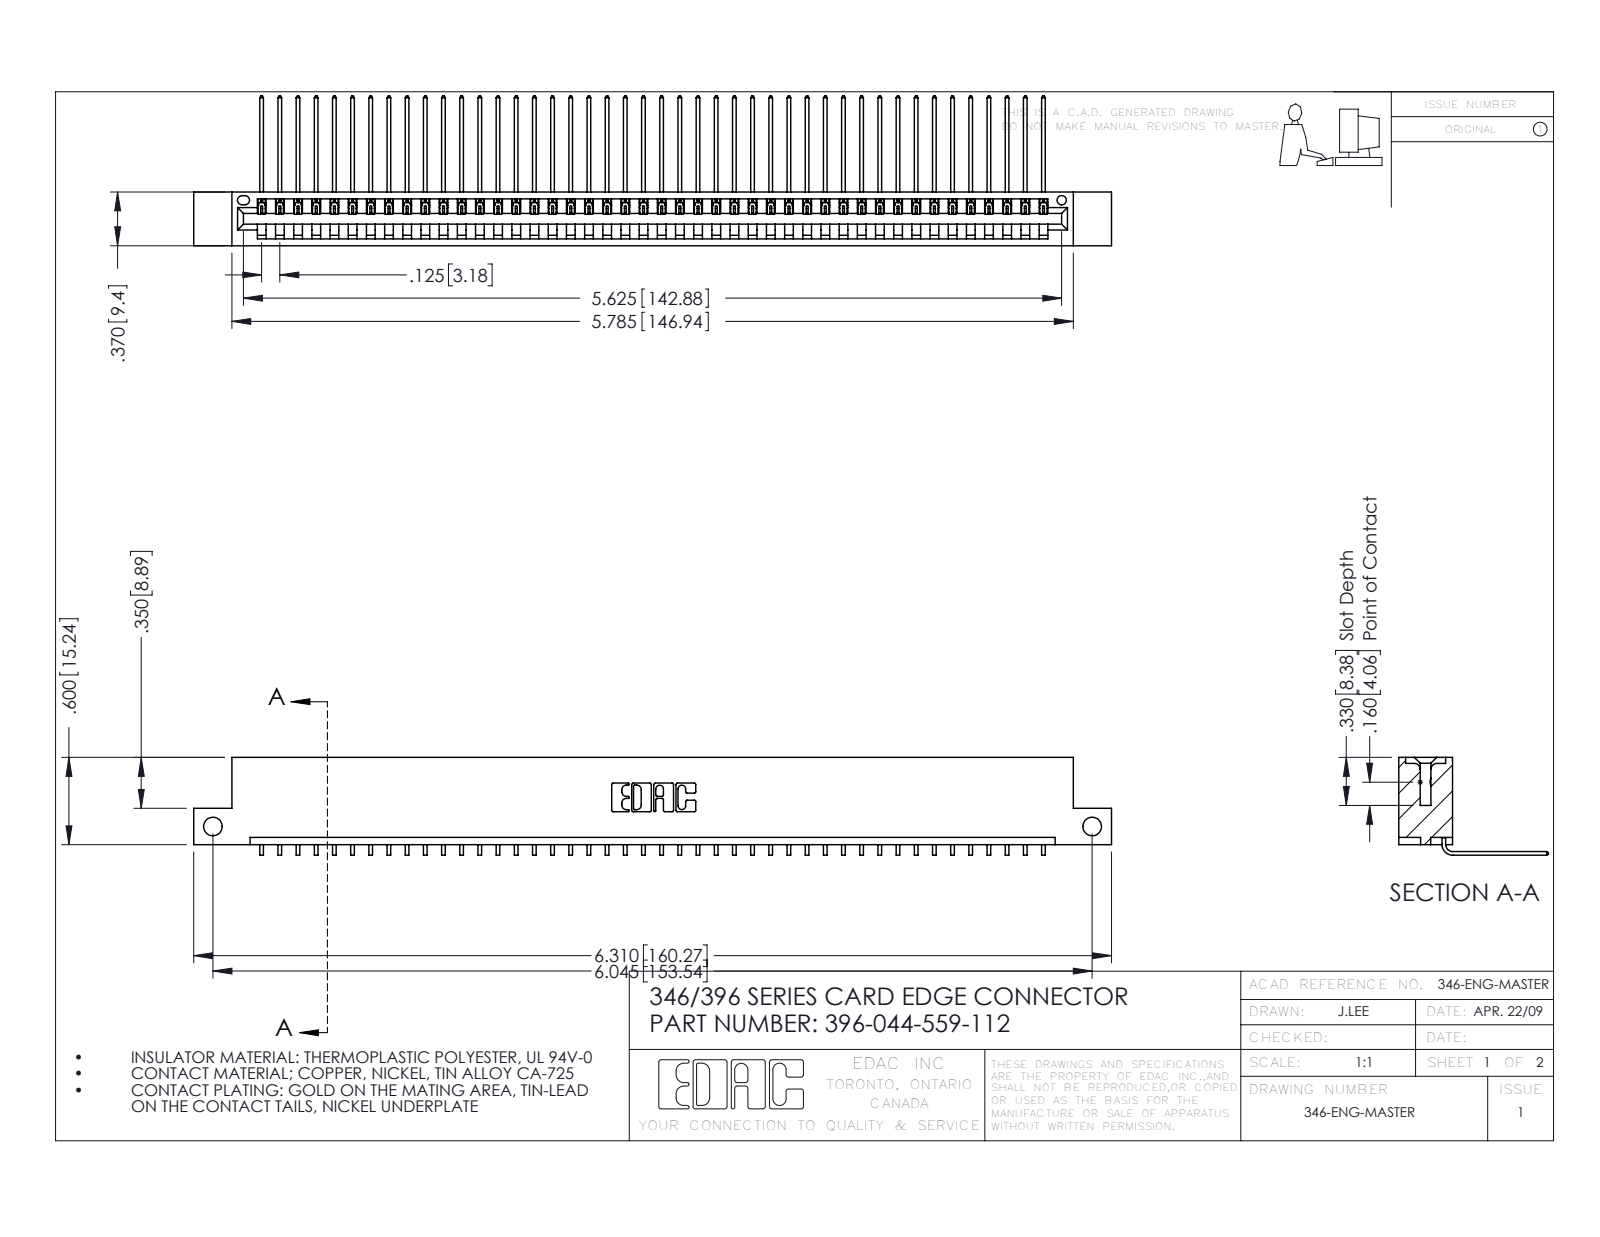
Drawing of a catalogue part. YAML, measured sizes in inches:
part_name: "396-044-559-112; 346 Part_Flush Mounting Lugs - Side Mount; 345-292-001_558 559 Tail - 1"
step_written_by: "SolidWorks 2016 (CONFIG_CONTROL_DESIGN)"
units: inches
bodies: {solids: 45, faces: 2762, planar: 1924, cylindrical: 838, other: 0}
overall_size: [6.31, 1.03, 0.673]
volume: 0.941
surface_area: 31.03
round_holes:
  - {diameter: 0.128, count: 2}
  - {diameter: 0.064, count: 1}
partial_cylinders:
  - {radius: 0.006, count: 88}
  - {radius: 0.01, count: 22}
  - {radius: 0.007, count: 6}
  - {radius: 0.031, count: 6}
  - {radius: 0.026, count: 3}
  - {radius: 0.031, count: 2}
  - {radius: 0.04, count: 2}
  - {radius: 0.014, count: 1}
face_to_face_distances: [0.048, 0.322, 0.37, 0.025, 0.25, 0.072, 0.298, 0.148, 0.222, 0.1]
hole_center_spacings: [6.045]
